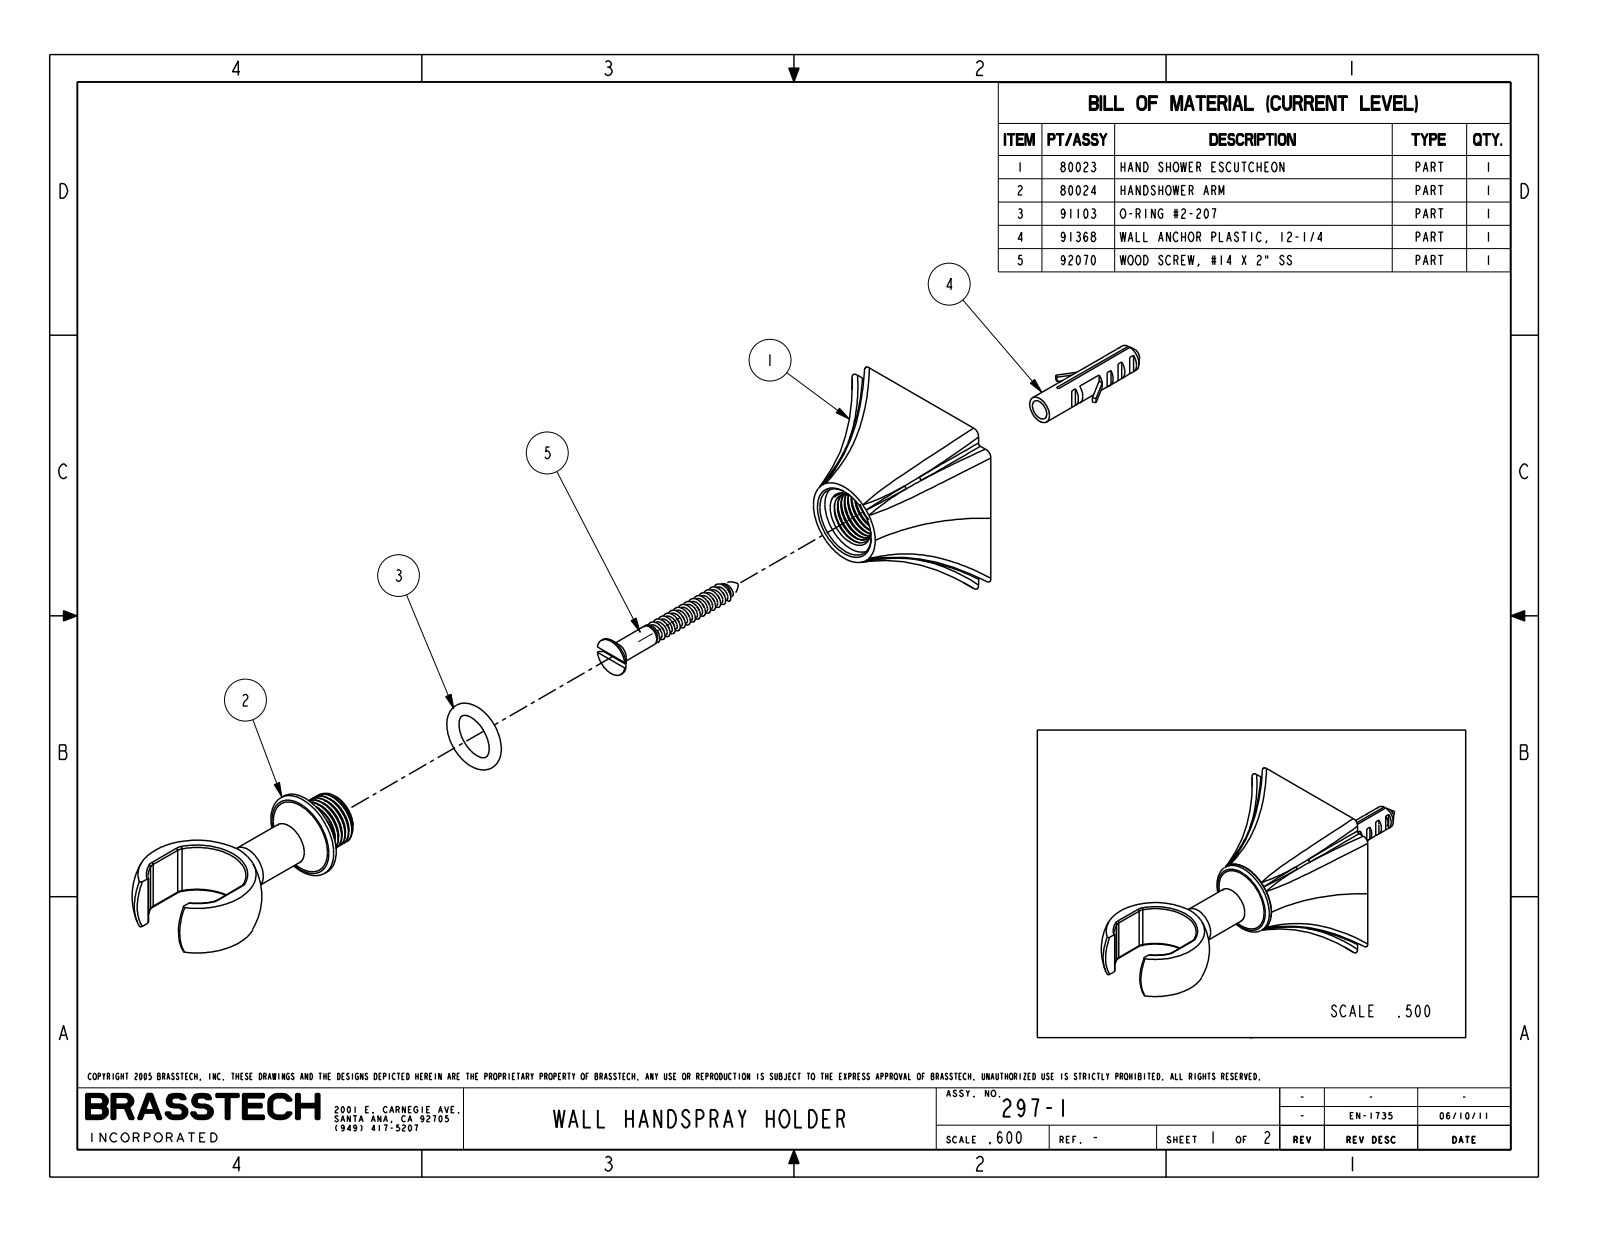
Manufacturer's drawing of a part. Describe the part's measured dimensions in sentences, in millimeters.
The part is named "297-1_WEB". Its 3-D file was written by "PRO/ENGINEER BY PARAMETRIC TECHNOLOGY CORPORATION, 2009300 (CONFIG_CONTROL_DESIGN)". It is 0 solids with 94 faces: 9 planar, 19 cylindrical and 66 other. Overall it measures 93.1 by 57.2 by 57.2 millimeters. Round bosses or shafts: 1 of diameter 52.1, 1 of diameter 25.4, 1 of diameter 12.7. Partial cylindrical surfaces (rounded edges, fillets, slot ends): 6 of radius 0.5, 4 of radius 3.2, 1 of radius 14.2. The main face-to-face distances are 34, 33.8, 15.9, 26, 4.4, 21.6, 17.1.
